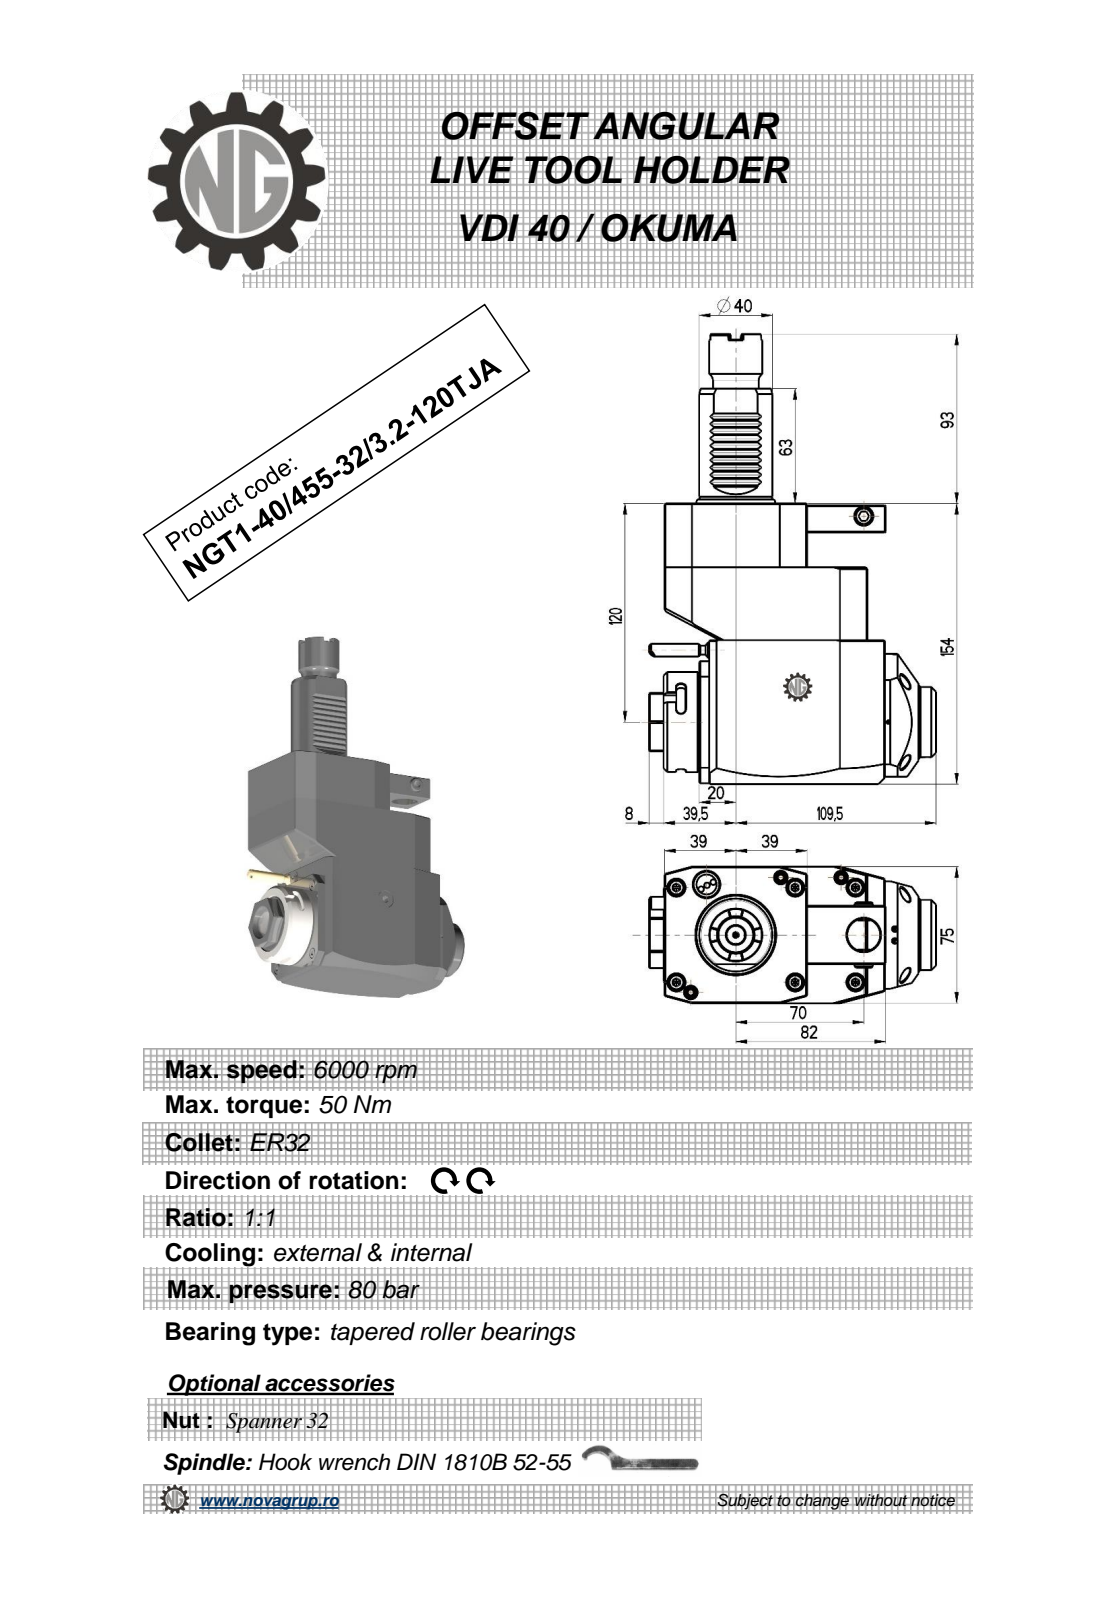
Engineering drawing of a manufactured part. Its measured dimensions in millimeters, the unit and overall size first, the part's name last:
Units: millimetres
Overall size (bounding box): 247 × 157 × 75
Round holes (diameter × count): ⌀2.5 ×1, ⌀3 ×1, ⌀9.5 ×1, ⌀18 ×1, ⌀23 ×1
Round bosses / shafts (diameter × count): ⌀8.96 ×2, ⌀55 ×1, ⌀48 ×1, ⌀40 ×1, ⌀38.5 ×1, ⌀29 ×1, ⌀25 ×1, ⌀10 ×1
Partial cylindrical surfaces — rounded edges, fillets, slot ends (radius × count): R0.3 ×10, R2.5 ×6, R180 ×2, R0.5 ×1, R4.25 ×1, R10 ×1, R24.5 ×1, R37.5 ×1
Main face-to-face distances: 75, 154, 19, 59, 0.5, 111, 92, 35, 119, 53.5
Hole centre spacings: 43.2, 75.07, 112.5
Volume: 1 308 000 mm³ · Surface area: 94 347 mm²
Bodies: 1 solid, 381 faces (205 planar, 68 cylindrical, 108 other)
Part name (STEP PRODUCT): NGT1_40_455_32_3_2_120TJA
STEP written by: PRO/ENGINEER BY PARAMETRIC TECHNOLOGY CORPORATION, 2010280 (CONFIG_CONTROL_DESIGN)
